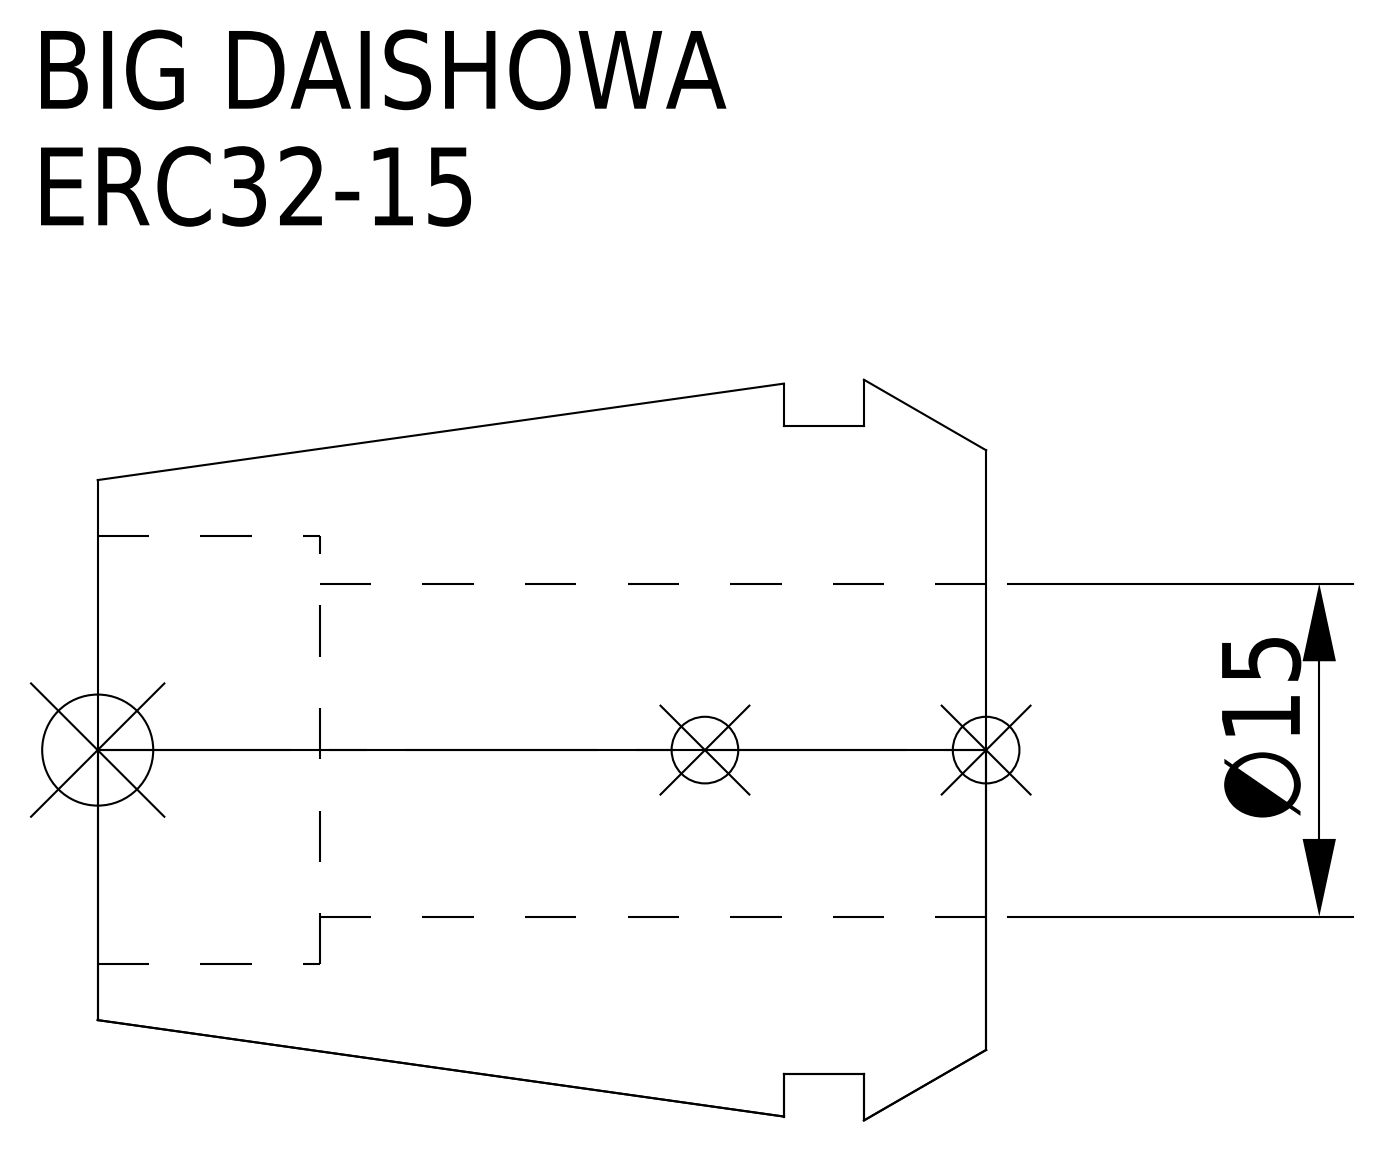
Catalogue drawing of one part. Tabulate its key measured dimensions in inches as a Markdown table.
| quantity | value |
| --- | --- |
| part name | ERC32-15 |
| STEP written by | CREO PARAMETRIC BY PTC INC, 2016380 (AUTOMOTIVE_DESIGN) |
| units | inches |
| bodies | 1 solid, 15 faces (5 planar, 6 cylindrical, 4 other) |
| overall size | 1.575 × 1.313 × 1.313 |
| volume | 1.112 in³ |
| surface area | 10.59 in² |
| round holes (diameter × count) | 0.591 × 1, 0.76 × 1 |
| round bosses / shafts (diameter × count) | 1.15 × 1 |
| main face-to-face distances | 0.217, 0.358, 0.142, 1.575, 1.358, 1.217, 1.181, 0.965, 0.823, 0.394 |
